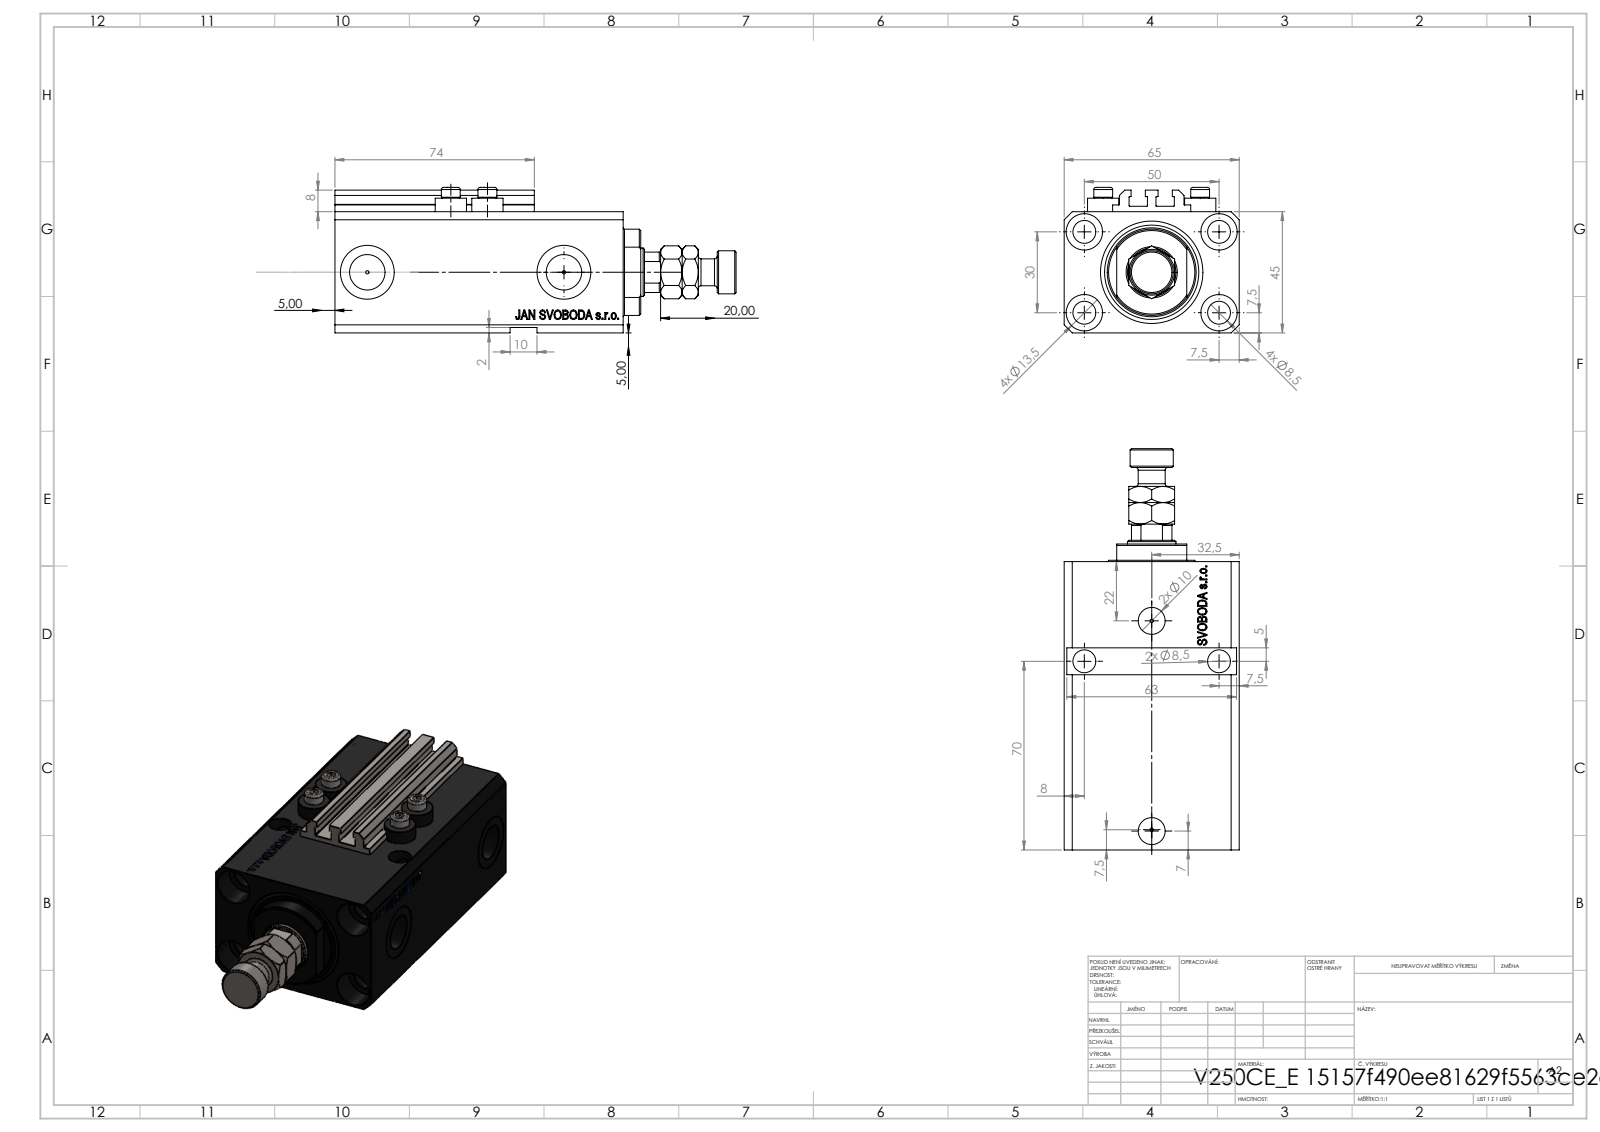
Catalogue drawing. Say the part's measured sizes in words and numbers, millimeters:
The part is named "MFA; ALLEN BOLT V250CE; V250CE_VC_E; V250CE_C_VCP (+1 more)". Its 3-D file was written by "SolidWorks 2019 (CONFIG_CONTROL_DESIGN)". It is 9 solids with 1155 faces: 531 planar, 162 cylindrical and 462 other. Overall it measures 149 by 65 by 54 millimeters. Its volume is 275 209 cubic millimeters and its surface area 80 077 square millimeters. Round holes: 9 of diameter 8.5, 4 of diameter 1.25, 4 of diameter 4, 4 of diameter 13.5, 2 of diameter 10, 2 of diameter 13.16, 2 of diameter 20, 1 of diameter 18, 1 of diameter 25, 1 of diameter 38. Round bosses or shafts: 4 of diameter 11.6, 4 of diameter 7, 1 of diameter 16, 1 of diameter 10. Partial cylindrical surfaces (rounded edges, fillets, slot ends): 10 of radius 0.2, 1 of radius 8.5, 1 of radius 16. The main face-to-face distances are 45, 65, 14, 93, 2, 47, 107, 6.9, 20.5, 24. The hole center spacings are 29.15, 50, 13.6, 14.76, 15.12, 27.51, 27.89, 30.
